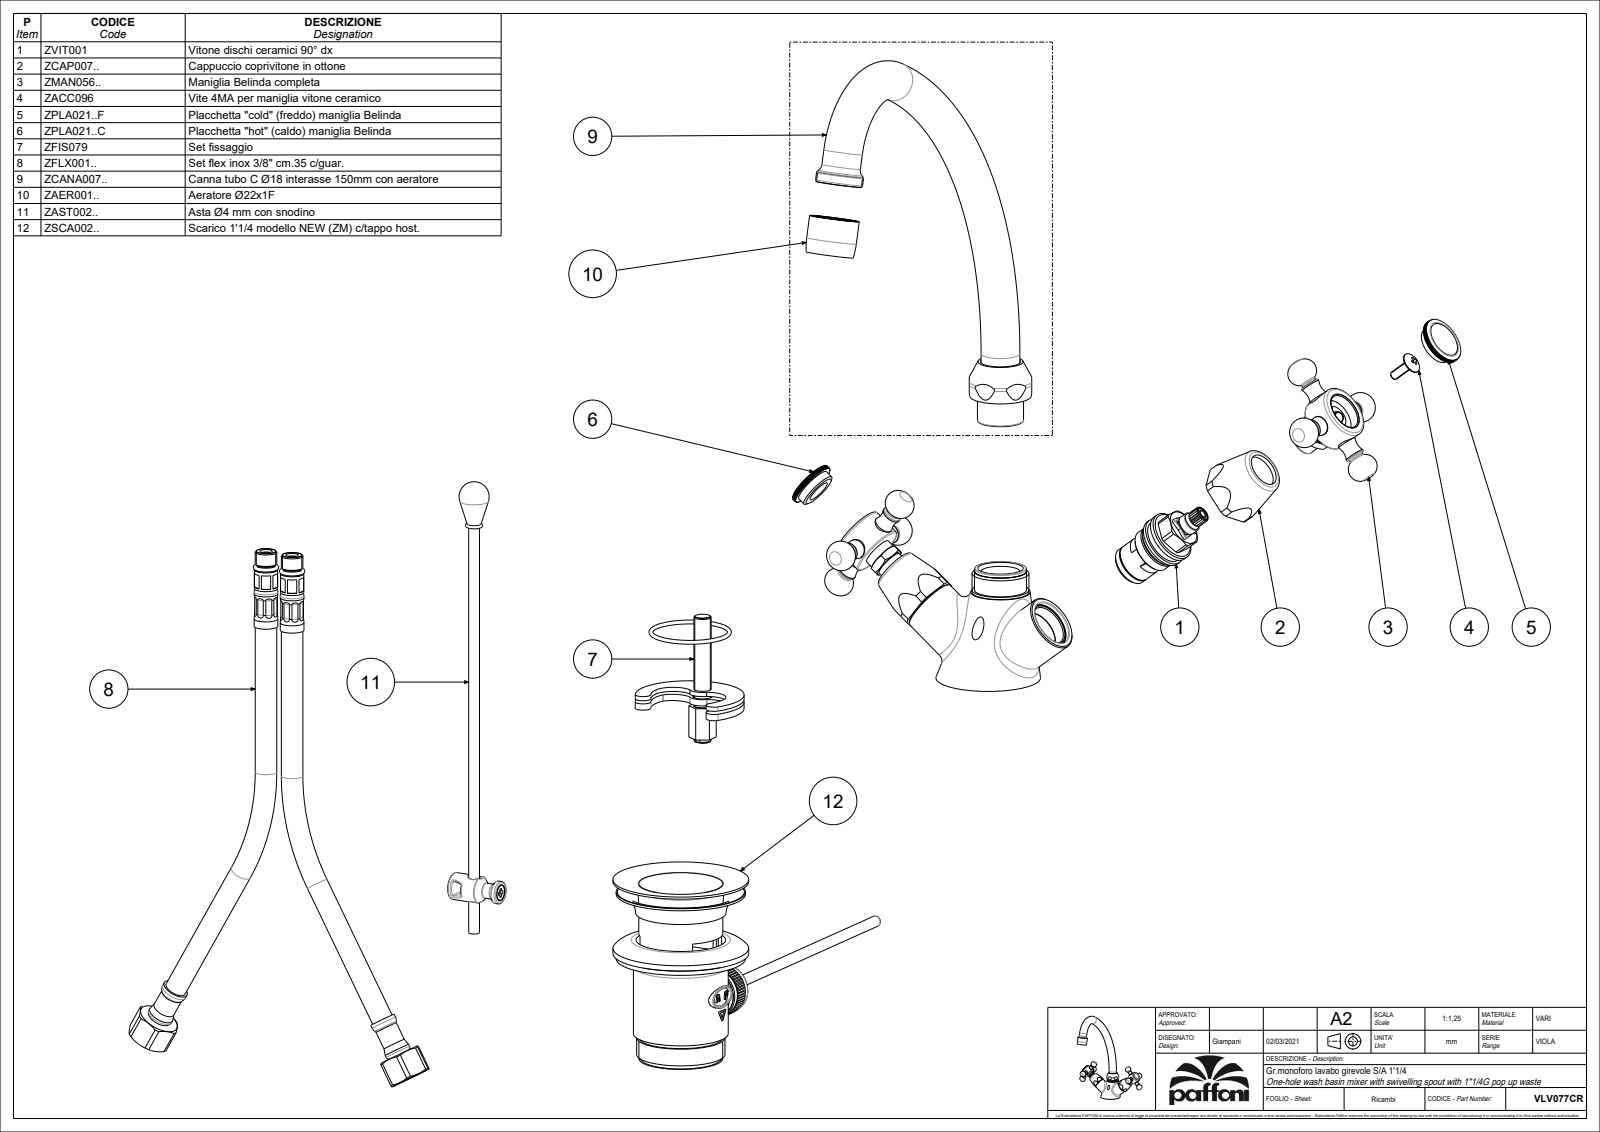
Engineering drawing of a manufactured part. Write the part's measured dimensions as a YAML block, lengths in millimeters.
part_name: "VLV077CR"
step_written_by: "CREO PARAMETRIC BY PTC INC, 2020044 (CONFIG_CONTROL_DESIGN)"
units: millimeters
bodies: {solids: 2, faces: 942, planar: 460, cylindrical: 294, other: 188}
overall_size: [228.5, 186.88, 175.57]
volume: 212365
surface_area: 44190
round_holes:
  - {diameter: 5.5, count: 1}
round_bosses_or_shafts:
  - {diameter: 9, count: 6}
  - {diameter: 7, count: 6}
  - {diameter: 26.3, count: 2}
  - {diameter: 25, count: 2}
  - {diameter: 18, count: 2}
  - {diameter: 14, count: 2}
  - {diameter: 13, count: 2}
  - {diameter: 26.4, count: 1}
partial_cylinders:
  - {radius: 11, count: 2}
  - {radius: 14.5, count: 2}
face_to_face_distances: [26.49, 11.2, 20.75, 35.21, 24.01, 26.5, 5.75, 16.5, 29, 5.74]
